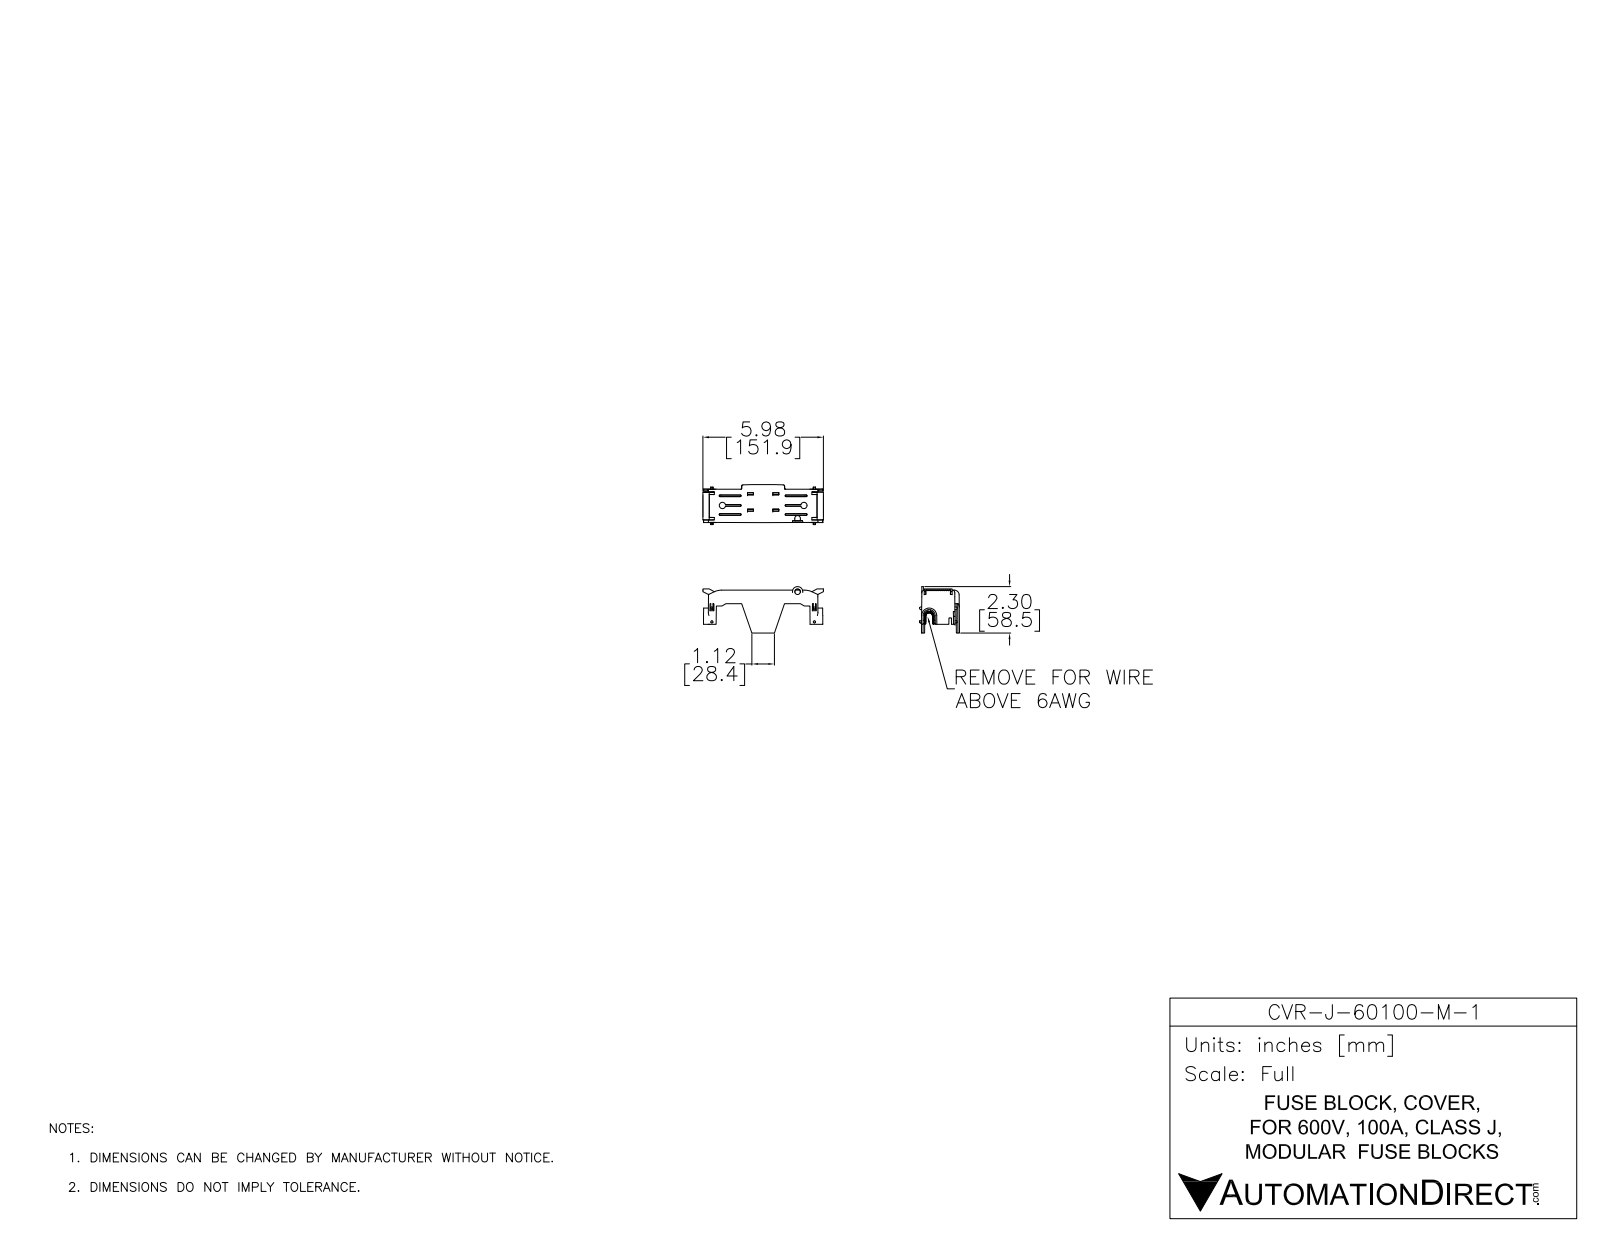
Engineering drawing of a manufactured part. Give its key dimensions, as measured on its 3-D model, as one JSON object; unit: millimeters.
{"part_name": "CVR-J-60100-M-1", "step_written_by": "SolidWorks 2017 (AUTOMOTIVE_DESIGN)", "units": "millimeters", "bodies": {"solids": 1, "faces": 1410, "planar": 917, "cylindrical": 102, "other": 391}, "overall_size": [151.9, 58.5, 50.4], "volume_mm3": 41790, "surface_area_mm2": 45170, "partial_cylinders_radius": [[1, 19], [3, 14], [0.8, 6], [1.5, 4], [0.3, 2], [0.5, 2], [3.5, 2], [4.3, 2]], "face_to_face_distances": [2, 5.5, 3.5, 7.5, 3, 8.8, 5, 6, 3.6, 1.5]}
